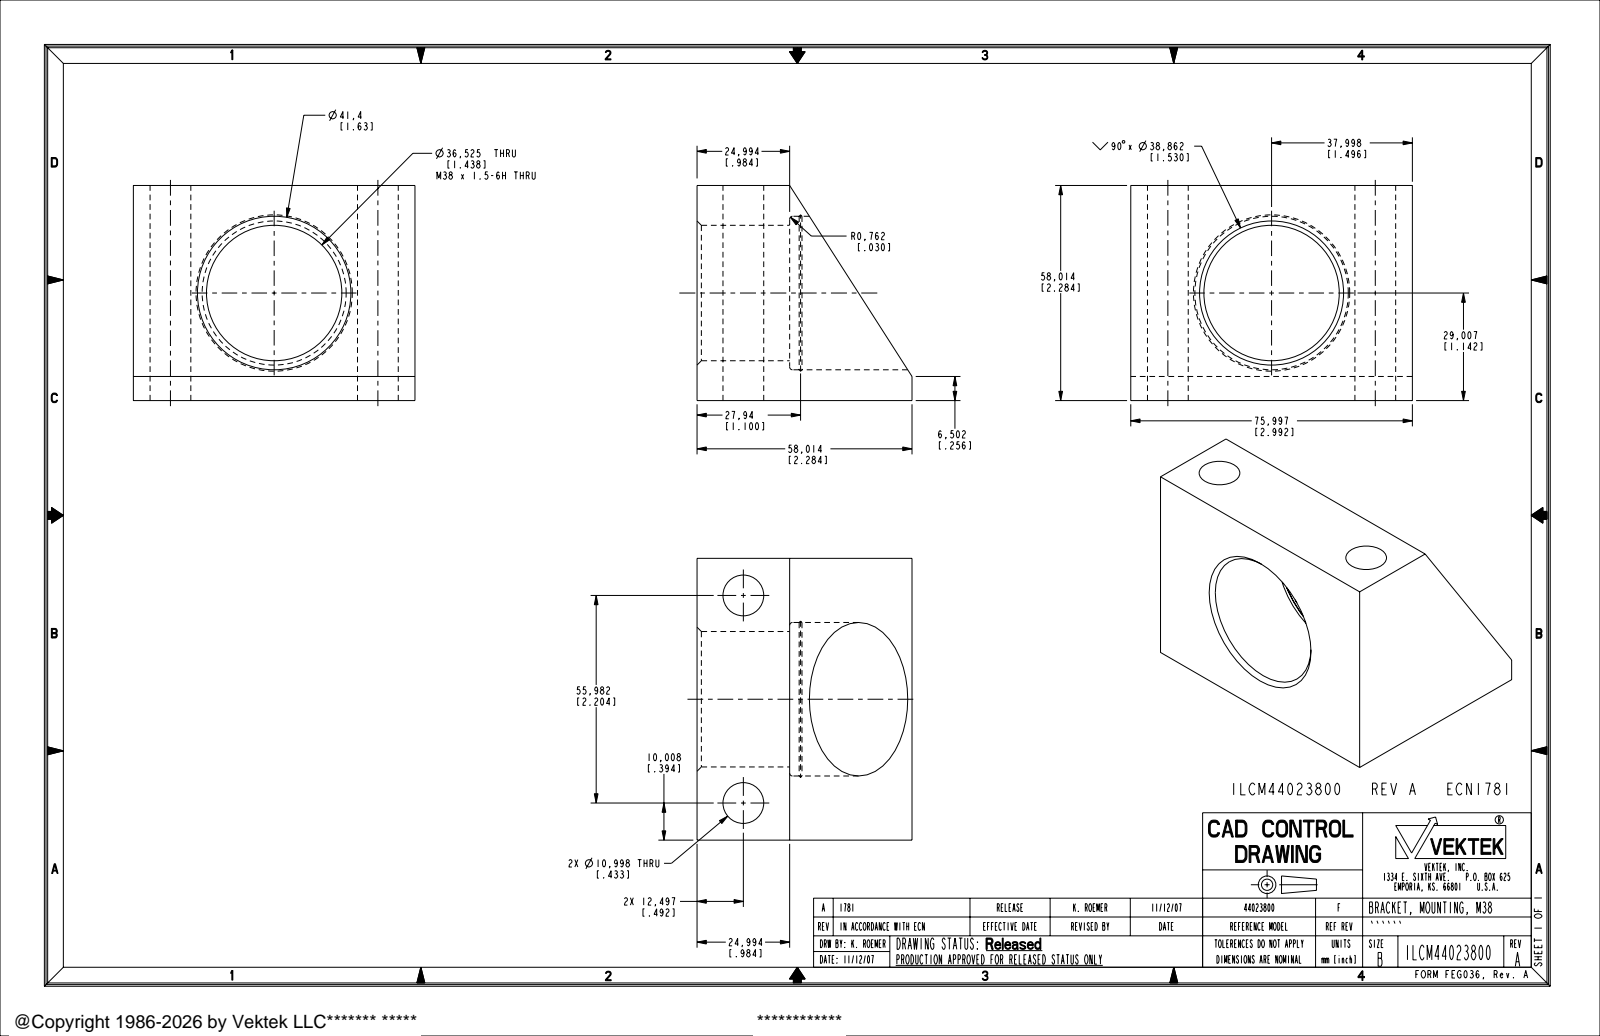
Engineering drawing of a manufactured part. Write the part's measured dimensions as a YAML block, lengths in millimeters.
part_name: "ILCM44023800"
step_written_by: "PRO/ENGINEER BY PARAMETRIC TECHNOLOGY CORPORATION, 2005180 (AUTOMOTIVE_DESIGN_CC2)"
units: millimeters
bodies: {solids: 1, faces: 26, planar: 8, cylindrical: 10, other: 8}
overall_size: [76, 58.01, 58.01]
volume: 128816
surface_area: 27381
round_holes:
  - {diameter: 11, count: 2}
  - {diameter: 36.52, count: 1}
  - {diameter: 41.4, count: 1}
face_to_face_distances: [76, 58.01, 24.99, 33.02]
hole_center_spacings: [55.98]
